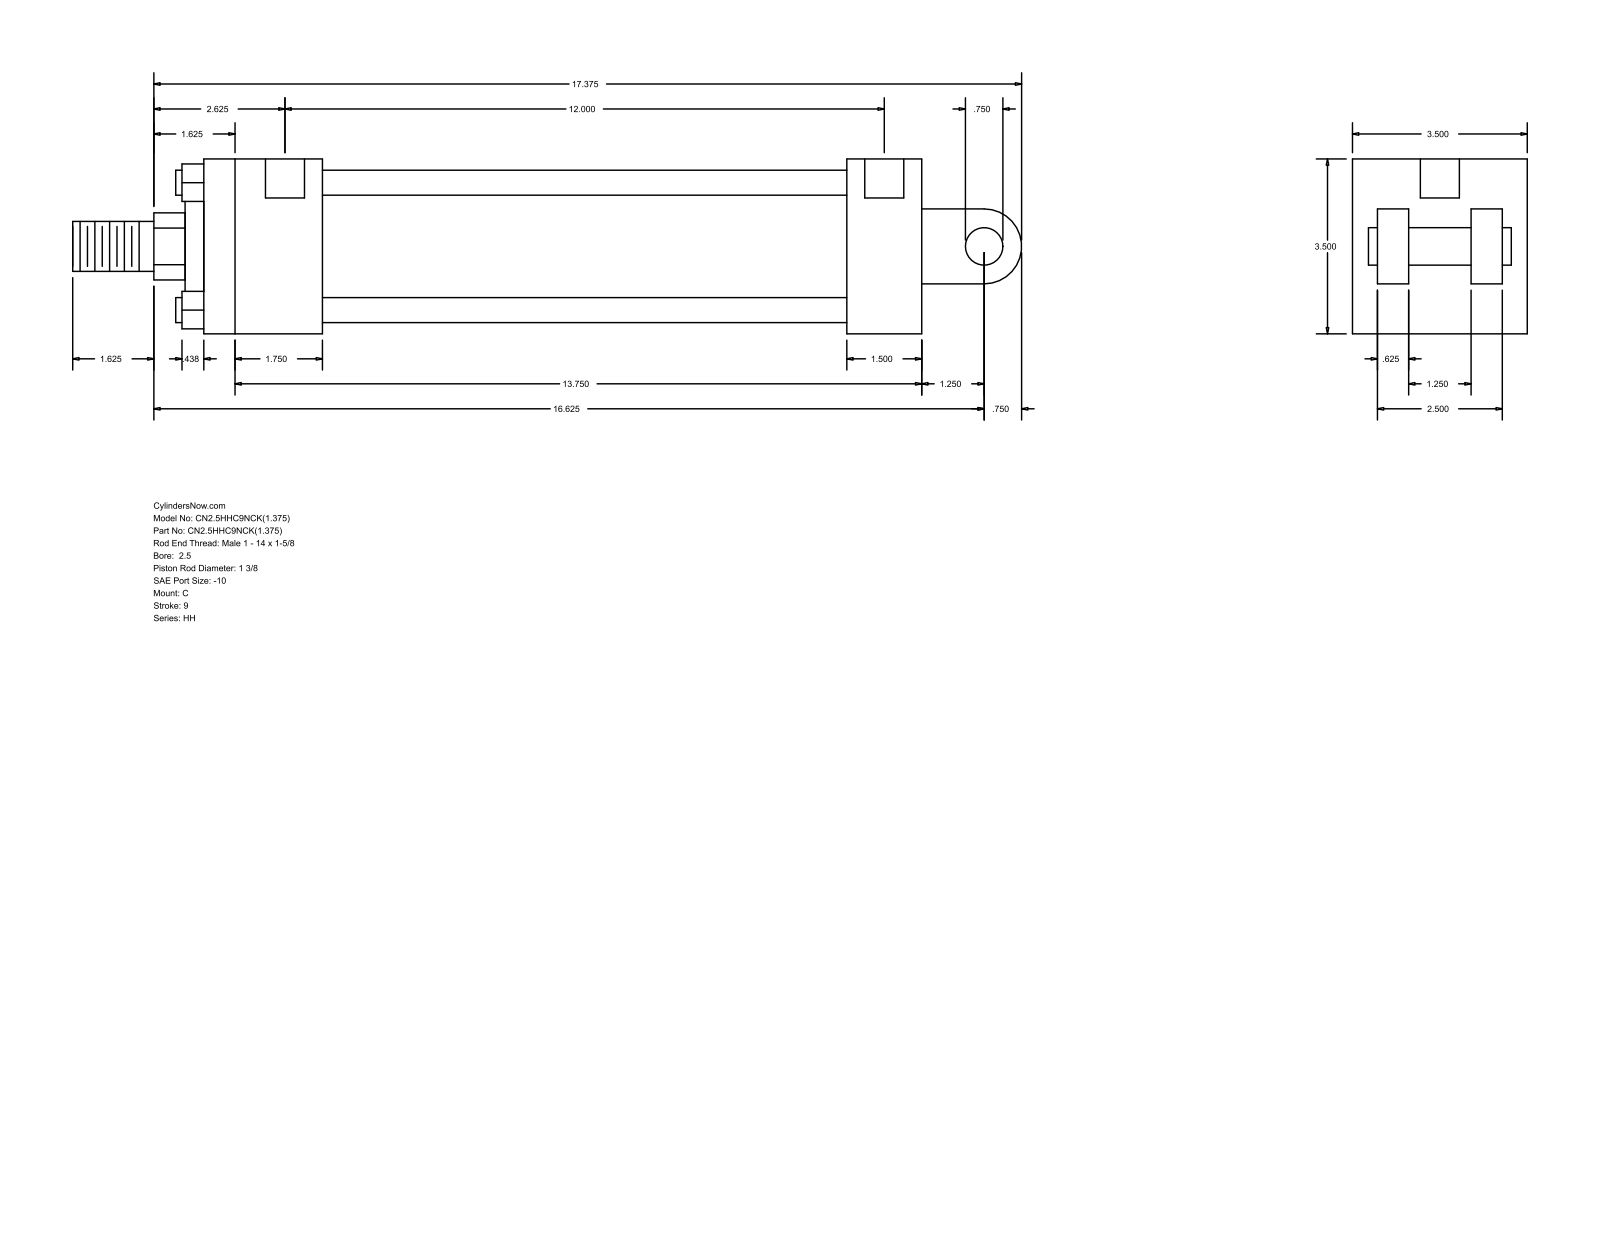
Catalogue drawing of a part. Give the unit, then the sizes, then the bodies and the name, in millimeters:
Units: millimetres
Overall size (bounding box): 482.6 × 88.9 × 88.9
Round holes (diameter × count): ⌀5.56 ×4, ⌀19.84 ×2
Round bosses / shafts (diameter × count): ⌀12.7 ×4, ⌀73.03 ×1, ⌀50.8 ×1, ⌀34.92 ×1, ⌀25.4 ×1, ⌀19.05 ×1
Partial cylindrical surfaces — rounded edges, fillets, slot ends (radius × count): R17.06 ×1, R19.05 ×1
Main face-to-face distances: 88.9, 365.12, 63.5, 12.7, 327.03, 38.09, 60.32, 266.71, 304.8, 76.2
Hole centre spacings: 1.58, 306.39, 307.97, 304.81
Bodies: 0 solids, 99 faces (70 planar, 29 cylindrical, 0 other)
Part name (STEP PRODUCT): HH_C__0250_1.375
STEP written by: GSSL Pune (CONFIG_CONTROL_DESIGN)
